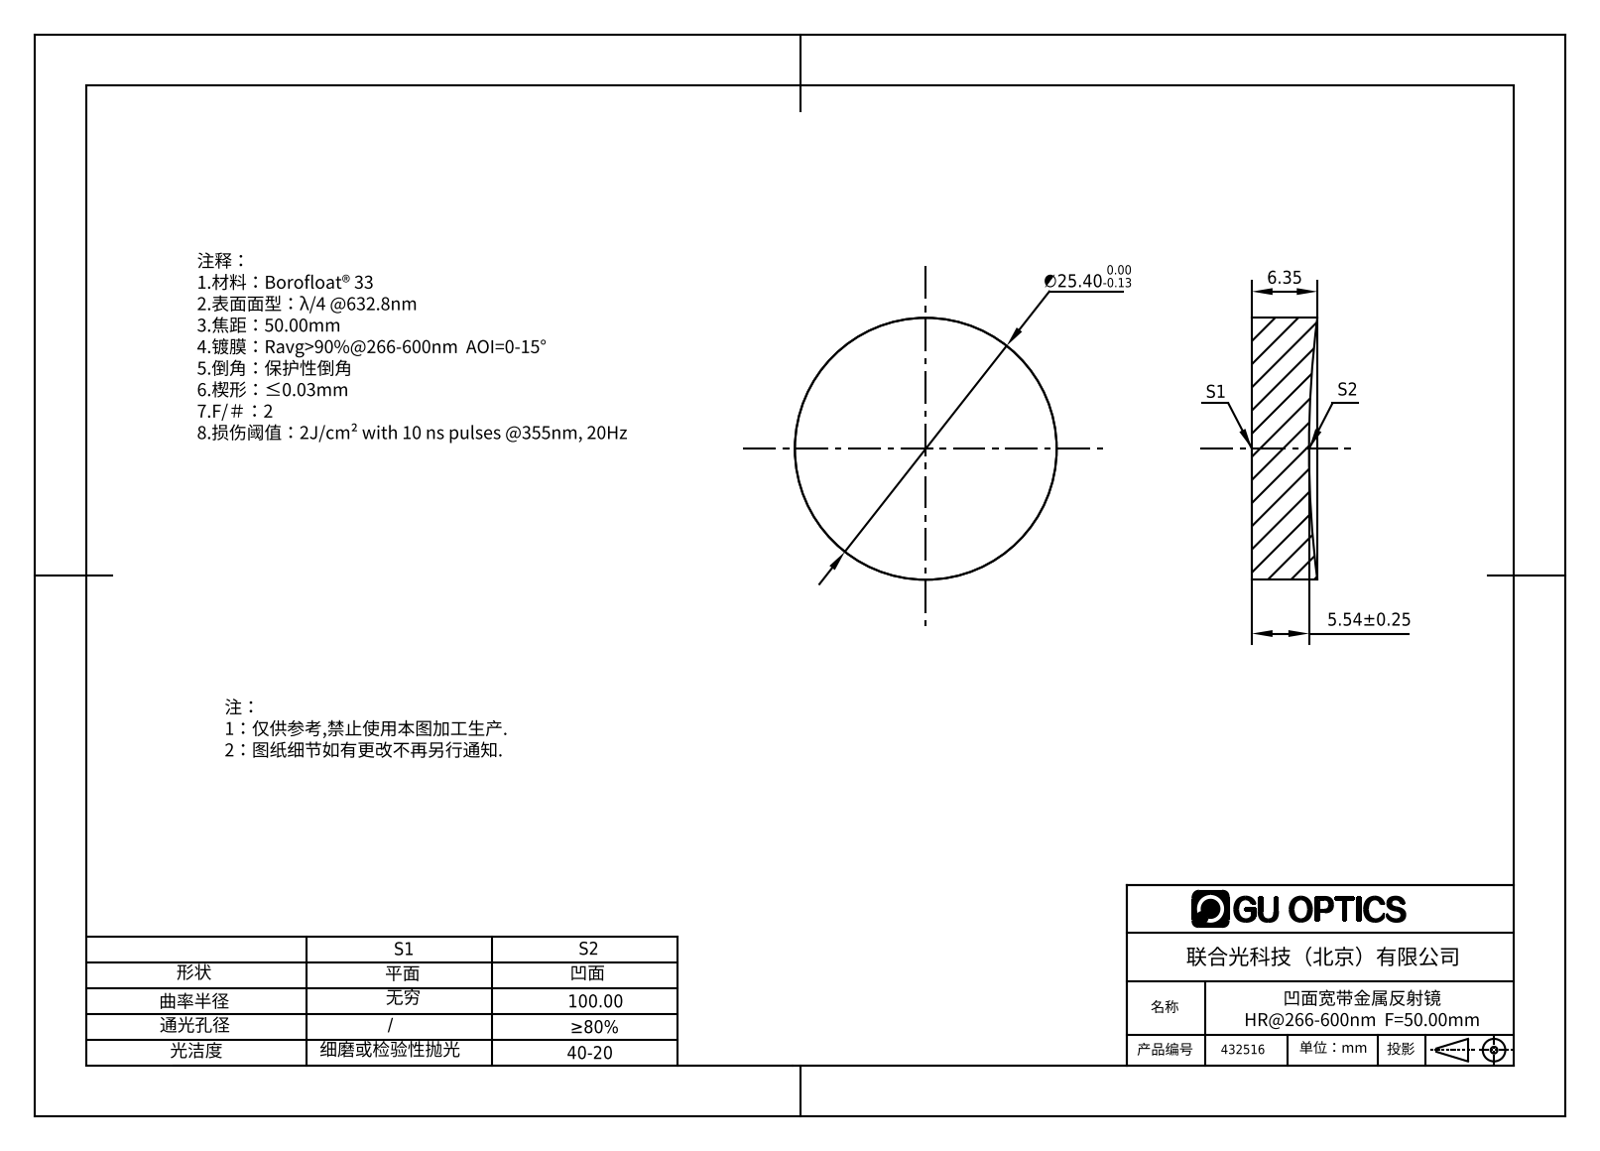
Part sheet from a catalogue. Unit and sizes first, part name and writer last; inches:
Units: inches
Overall size (bounding box): 1 × 1 × 0.25
Round bosses / shafts (diameter × count): ⌀1 ×1
Volume: 0.184 in³ · Surface area: 2.359 in²
Bodies: 1 solid, 5 faces (1 planar, 2 cylindrical, 2 other)
Part name (STEP PRODUCT): 432516
STEP written by: SolidWorks 2016 (AUTOMOTIVE_DESIGN)
